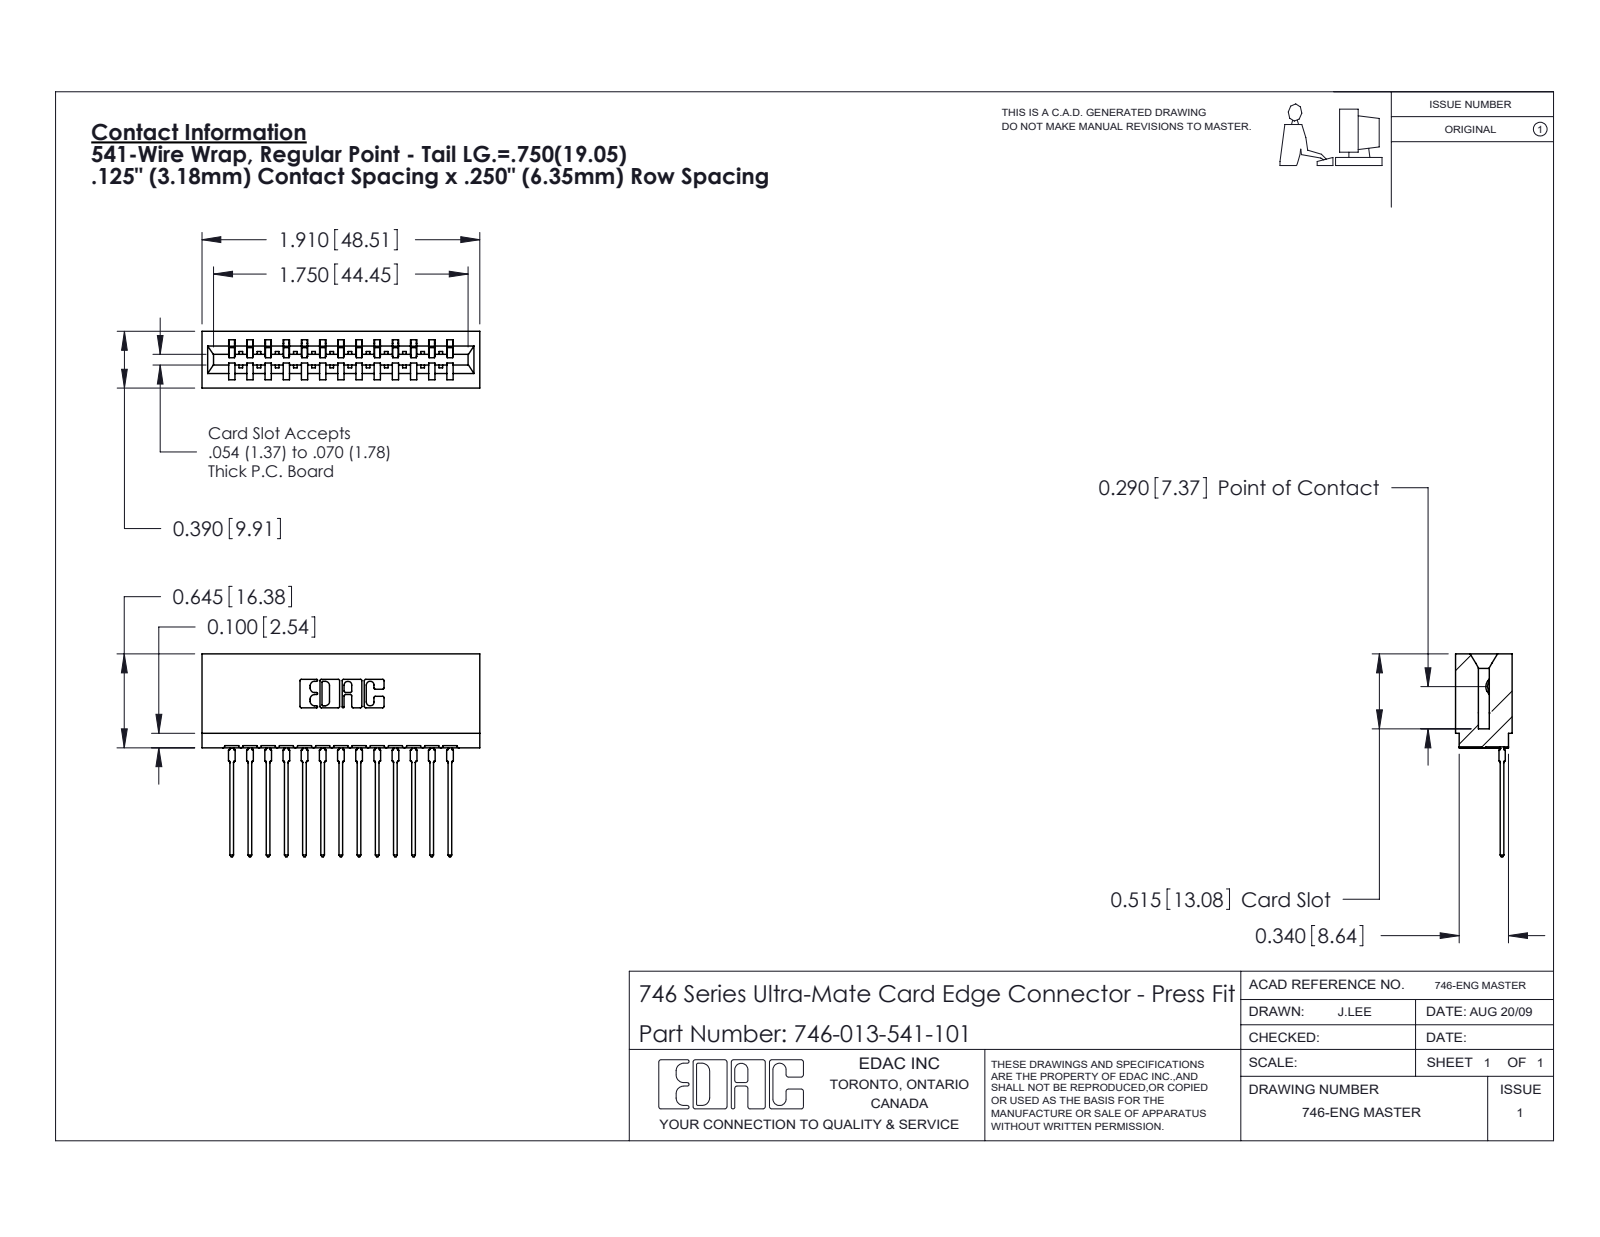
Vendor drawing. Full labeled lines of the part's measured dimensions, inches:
Part name (STEP PRODUCT): 746-013-541-101; 746-292-001_541; 746 Part_.515 Slot Depth - 01
STEP written by: SolidWorks 2020 (CONFIG_CONTROL_DESIGN)
Units: inches
Bodies: 14 solids, 1501 faces (874 planar, 289 cylindrical, 338 other)
Overall size (bounding box): 1.91 × 1.394 × 0.39
Volume: 0.325 in³ · Surface area: 11.97 in²
Partial cylindrical surfaces — rounded edges, fillets, slot ends (radius × count): R0.021 ×26, R0.01 ×22, R0.015 ×14, R0.007 ×6, R0.031 ×6, R0.005 ×4, R0.011 ×4, R0.026 ×3
Main face-to-face distances: 0.25, 0.333, 0.057, 0.5, 0.39, 0.125, 0.083, 0.125, 0.042, 0.208
